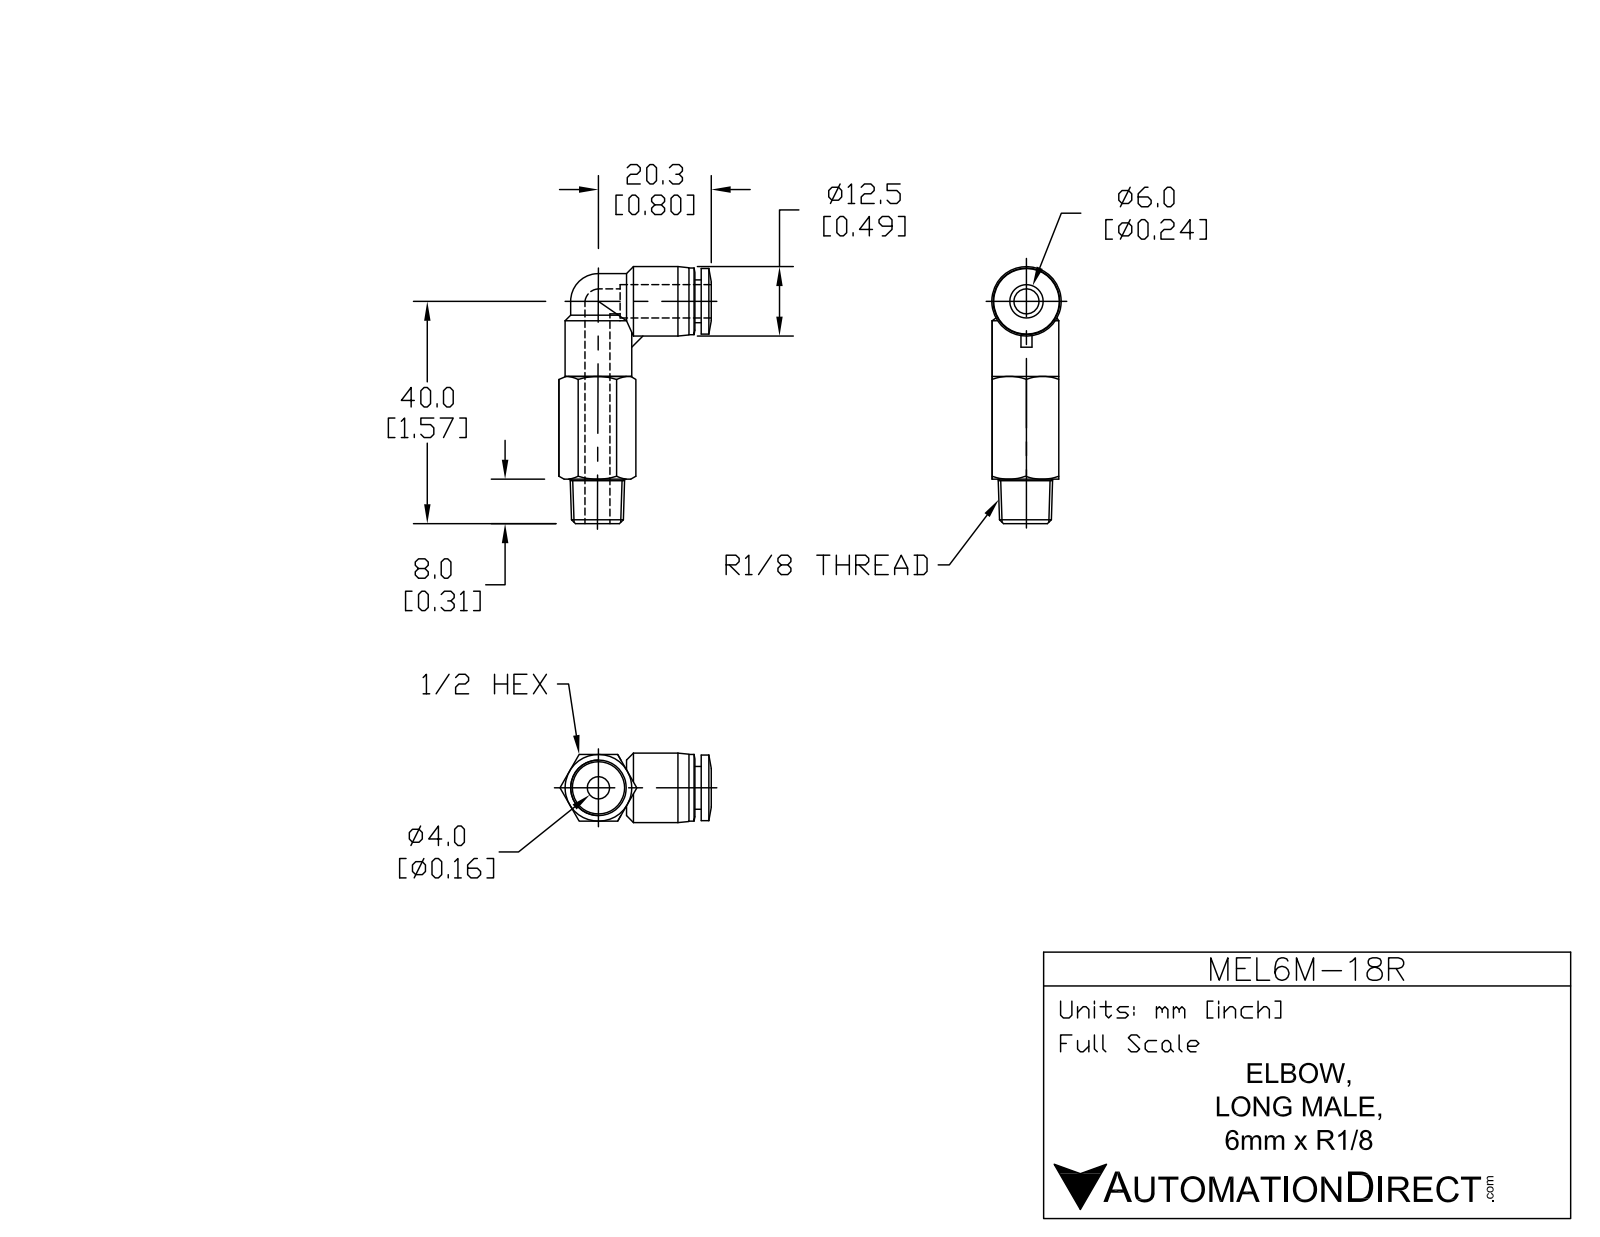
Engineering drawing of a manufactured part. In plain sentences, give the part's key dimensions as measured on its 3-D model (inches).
The part is named "MEL6M-18R". Its 3-D file was written by "SolidWorks 2015 (AUTOMOTIVE_DESIGN)". It is 1 solid with 66 faces: 16 planar, 19 cylindrical and 31 other. Overall it measures 1.821 by 1.072 by 0.492 inches. Its volume is 0.322 cubic inches and its surface area 5.258 square inches. Round holes: 2 of diameter 0.157, 1 of diameter 0.248. Round bosses or shafts: 2 of diameter 0.472, 1 of diameter 0.492, 1 of diameter 0.465, 1 of diameter 0.303. Partial cylindrical surfaces (rounded edges, fillets, slot ends): 2 of radius 0.197. The main face-to-face distances are 0.472, 0.045, 0.315, 0.53, 0.575, 0.197, 0.276, 0.646, 0.116, 0.071.
